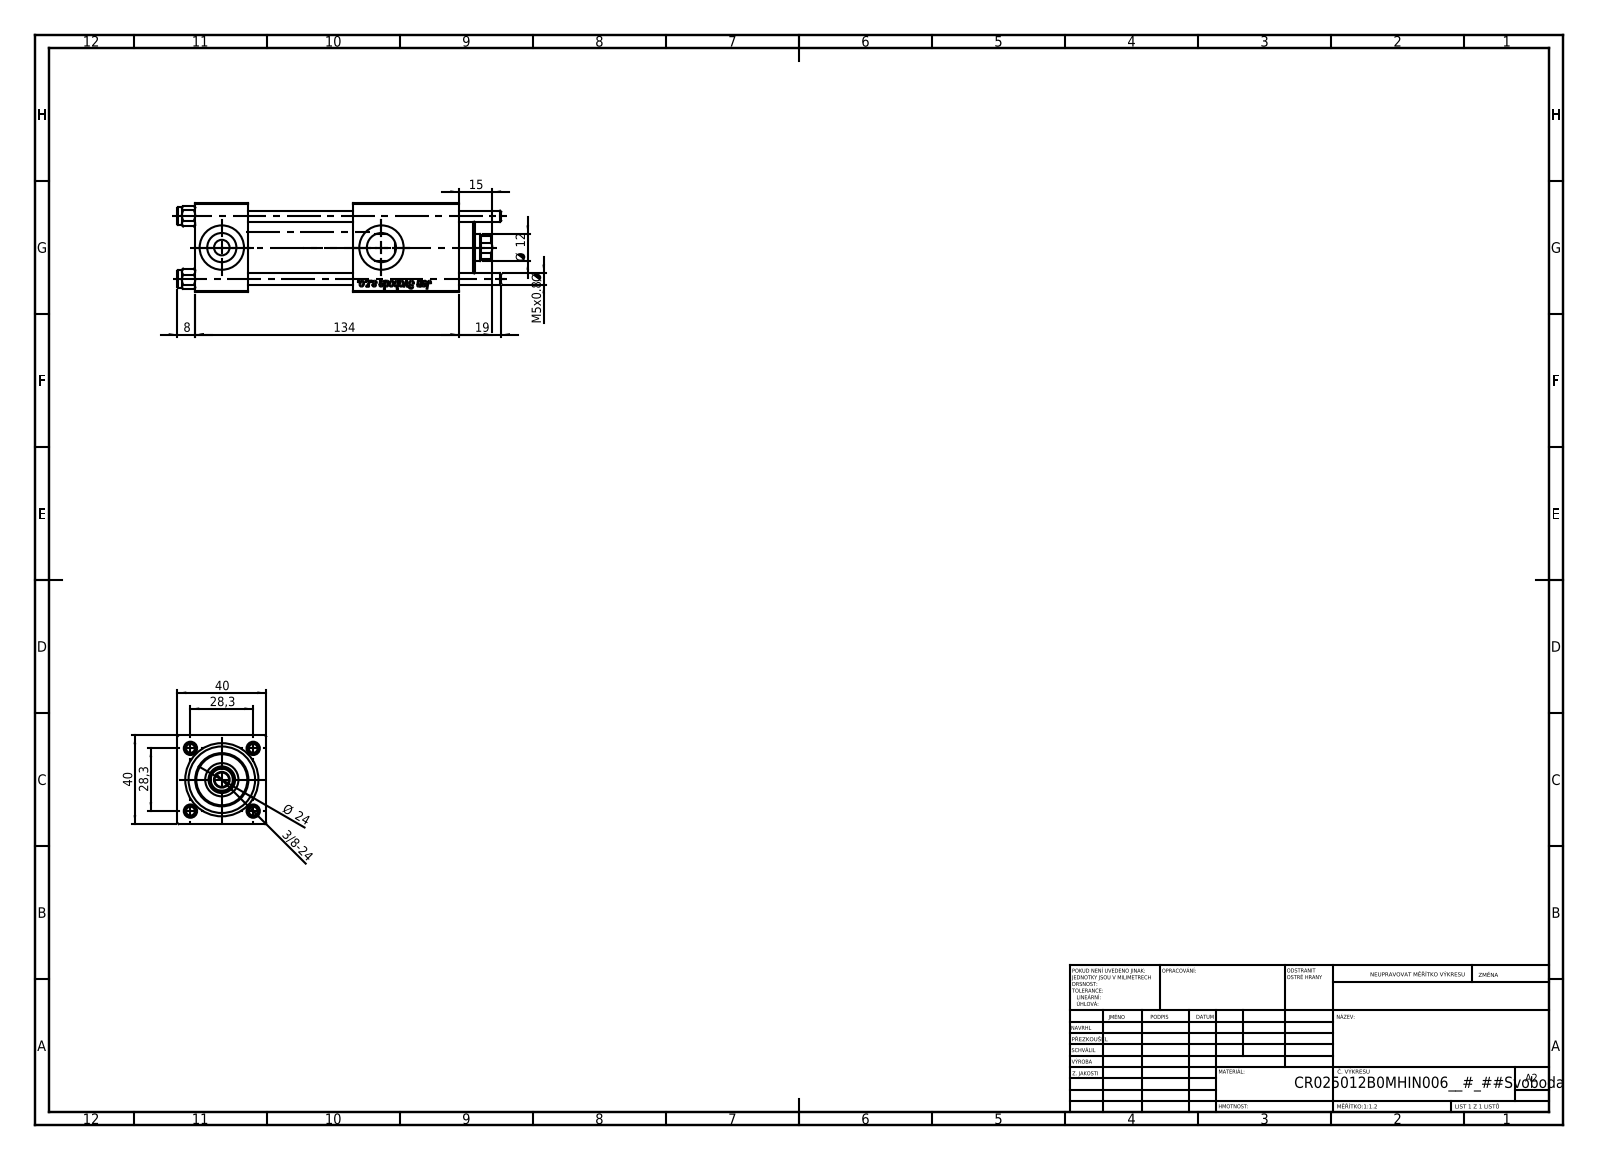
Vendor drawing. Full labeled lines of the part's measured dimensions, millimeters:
Part name (STEP PRODUCT): V215CR_VCP_B; V215_VC_A; V215CR_B-1; NUT_M5_B (+1 more)
STEP written by: SolidWorks 2019 (CONFIG_CONTROL_DESIGN)
Units: millimetres
Bodies: 11 solids, 1155 faces (429 planar, 78 cylindrical, 648 other)
Overall size (bounding box): 146 × 40 × 40
Volume: 144 884 mm³ · Surface area: 58 619 mm²
Round holes (diameter × count): ⌀5 ×4, ⌀20 ×3, ⌀7 ×2, ⌀13.16 ×2, ⌀6.5 ×1, ⌀12 ×1, ⌀15 ×1, ⌀25 ×1, ⌀30 ×1
Round bosses / shafts (diameter × count): ⌀8 ×4, ⌀31 ×1, ⌀24 ×1
Partial cylindrical surfaces — rounded edges, fillets, slot ends (radius × count): R5.5 ×1
Main face-to-face distances: 40, 24, 90.3, 66.3, 71, 47, 19.3, 119, 95, 48
Hole centre spacings: 20.01, 28.3, 40.02, 72
